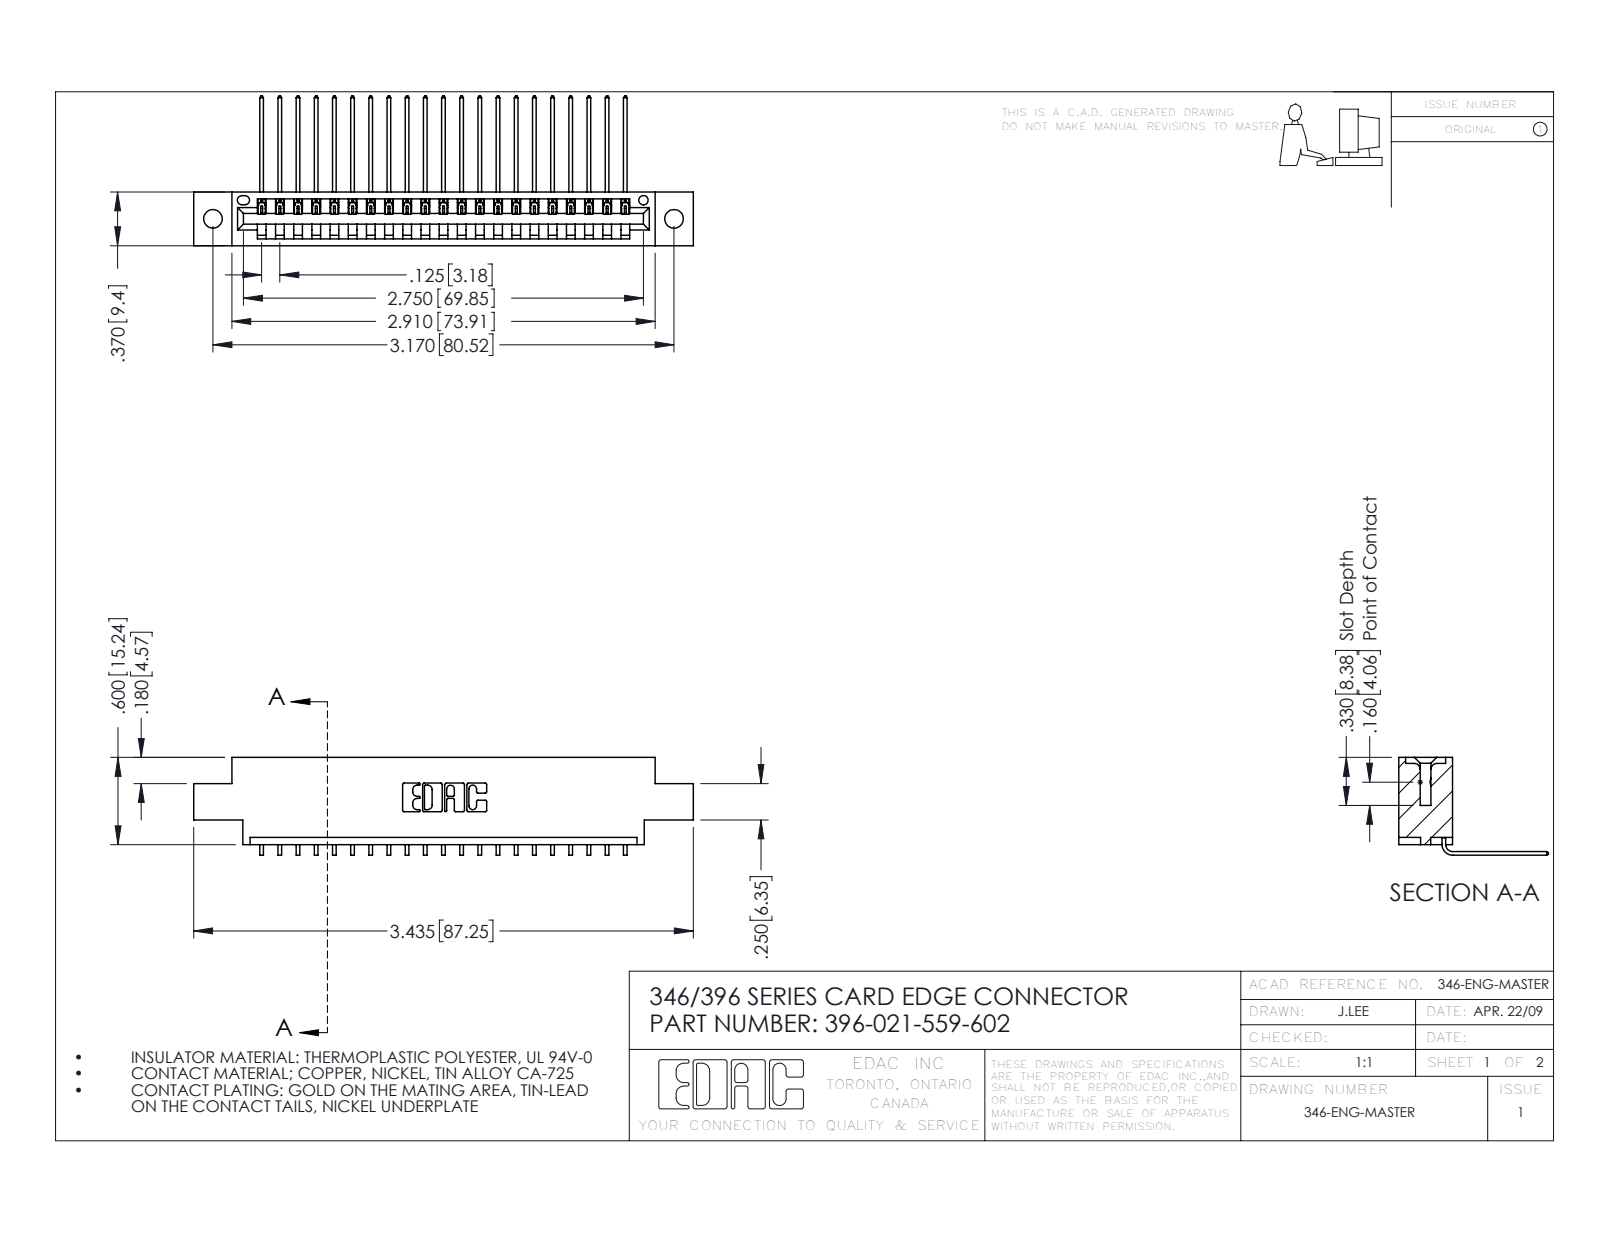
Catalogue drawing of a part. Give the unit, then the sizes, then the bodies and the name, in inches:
Units: inches
Overall size (bounding box): 3.435 × 1.03 × 0.673
Round holes (diameter × count): ⌀0.128 ×2, ⌀0.064 ×1
Partial cylindrical surfaces — rounded edges, fillets, slot ends (radius × count): R0.006 ×42, R0.01 ×22, R0.007 ×6, R0.031 ×6, R0.026 ×3, R0.031 ×2, R0.04 ×2, R0.014 ×1
Main face-to-face distances: 0.048, 0.37, 0.322, 0.25, 0.025, 0.072, 0.148, 0.222, 0.1, 0.174
Hole centre spacings: 0.246, 2.963, 3.17
Volume: 0.493 in³ · Surface area: 15.79 in²
Bodies: 22 solids, 1386 faces (962 planar, 424 cylindrical, 0 other)
Part name (STEP PRODUCT): 345-292-001_558 559 Tail - 1; 346 Part_0.170 Offset - 0.128 Dia; 396-021-559-602
STEP written by: SolidWorks 2016 (CONFIG_CONTROL_DESIGN)
